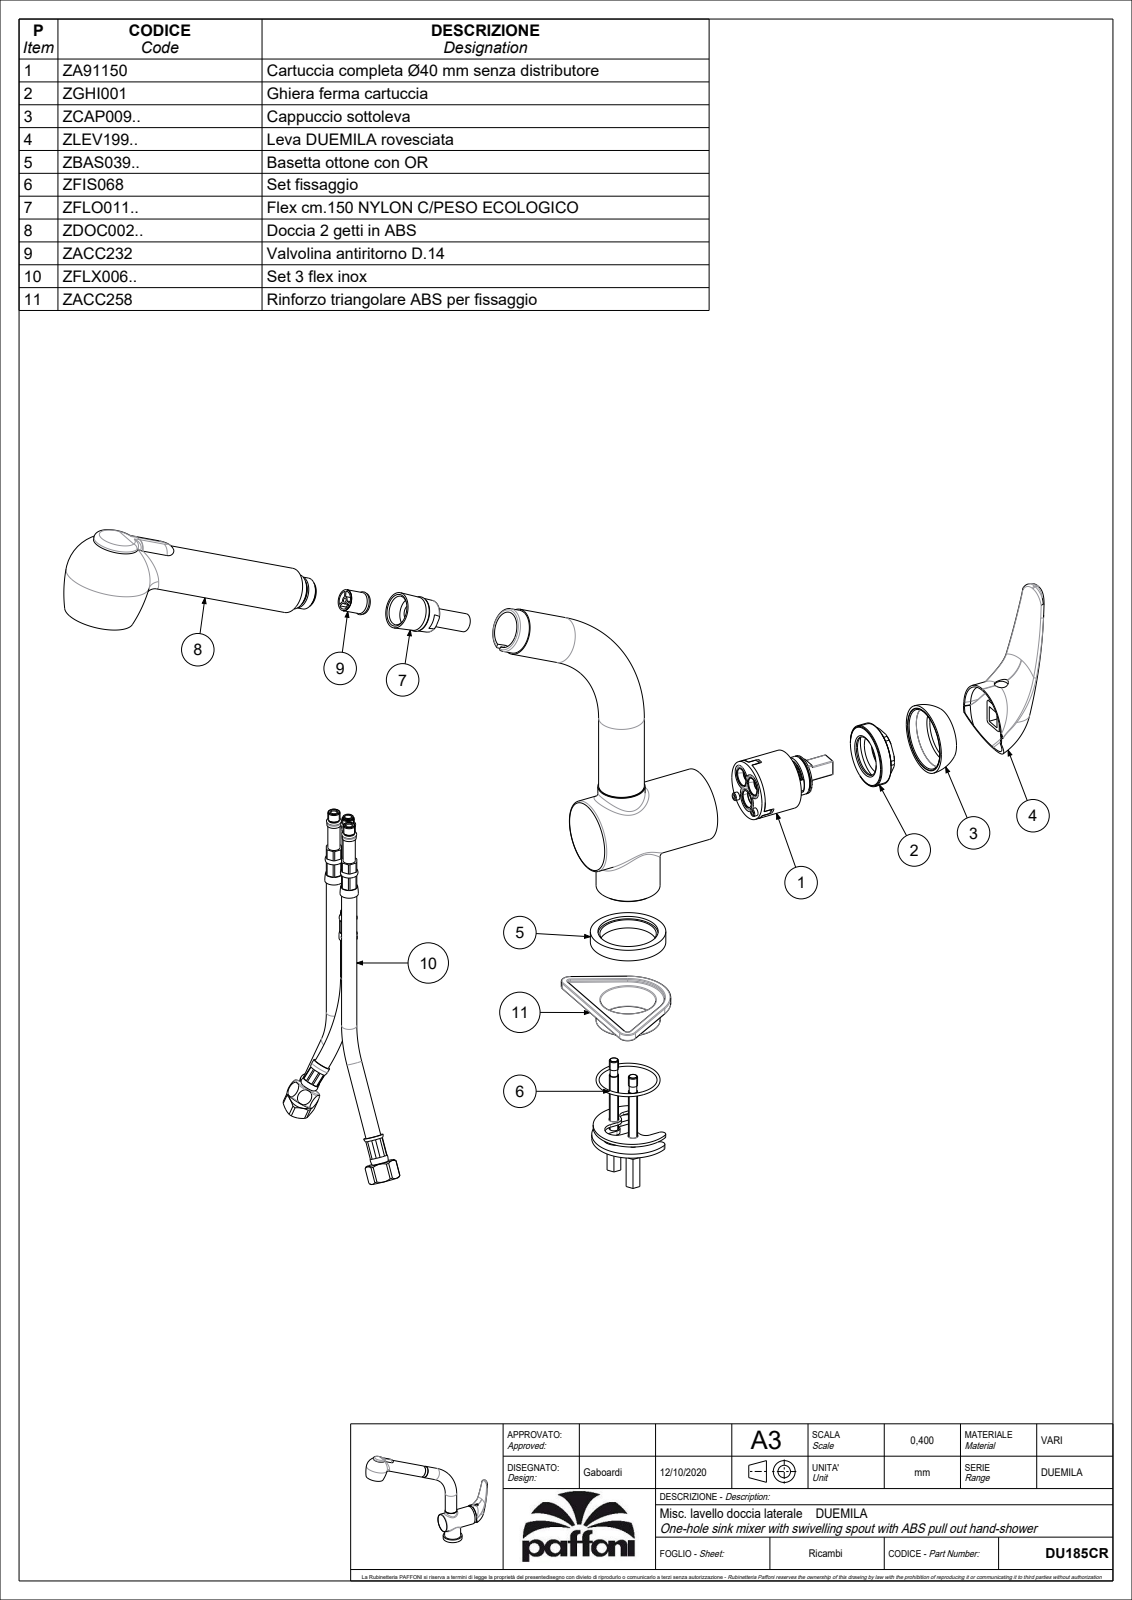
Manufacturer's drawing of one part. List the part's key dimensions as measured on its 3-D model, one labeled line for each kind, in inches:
Part name (STEP PRODUCT): DU185CR
STEP written by: CREO PARAMETRIC BY PTC INC, 2020044 (CONFIG_CONTROL_DESIGN)
Units: inches
Bodies: 0 solids, 180 faces (50 planar, 56 cylindrical, 74 other)
Overall size (bounding box): 14.149 × 12.159 × 2.205
Round holes (diameter × count): ⌀0.362 ×1, ⌀0.63 ×1
Round bosses / shafts (diameter × count): ⌀1.181 ×2, ⌀0.197 ×2, ⌀1.949 ×1, ⌀1.89 ×1, ⌀1.654 ×1, ⌀1.22 ×1, ⌀1.173 ×1, ⌀1.161 ×1
Partial cylindrical surfaces — rounded edges, fillets, slot ends (radius × count): R0.591 ×3, R0.059 ×2, R0.315 ×2, R0.945 ×2, R0.965 ×2, R0.079 ×1, R0.453 ×1, R0.709 ×1
Main face-to-face distances: 0.315, 0.571, 3.319, 3.004, 0.335, 0.138, 0.197, 0.118, 2.322, 2.204
